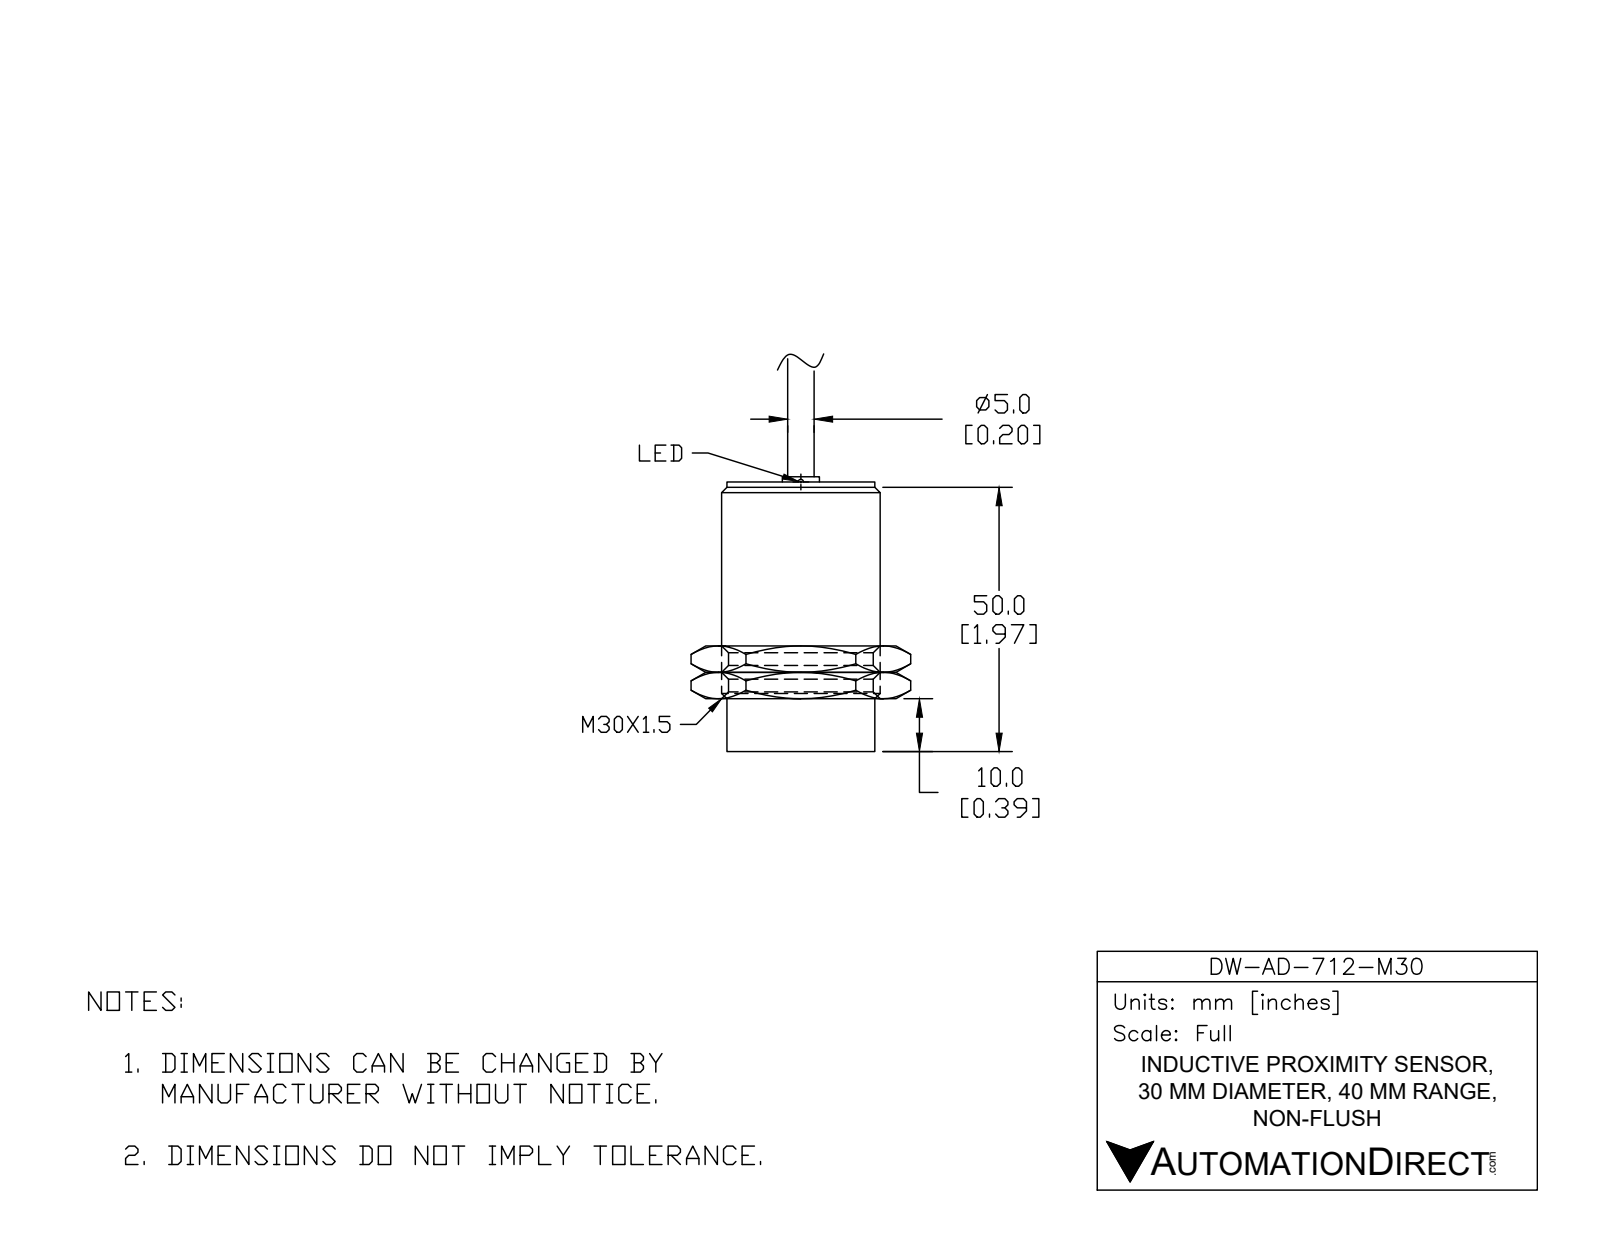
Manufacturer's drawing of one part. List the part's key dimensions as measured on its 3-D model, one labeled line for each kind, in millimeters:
Part name (STEP PRODUCT): DW-AD-712-M30
STEP written by: SolidWorks 2017 (AUTOMOTIVE_DESIGN)
Units: millimetres
Bodies: 2 solids, 37 faces (18 planar, 7 cylindrical, 12 other)
Overall size (bounding box): 76.6 × 30 × 30
Volume: 35 380 mm³ · Surface area: 6 516 mm²
Round bosses / shafts (diameter × count): ⌀30 ×1, ⌀27.5 ×1, ⌀10.5 ×1, ⌀6.8 ×1, ⌀5 ×1, ⌀3 ×1
Main face-to-face distances: 51, 0.8, 53, 2, 51.8, 1.2, 48, 3, 3.8, 5
